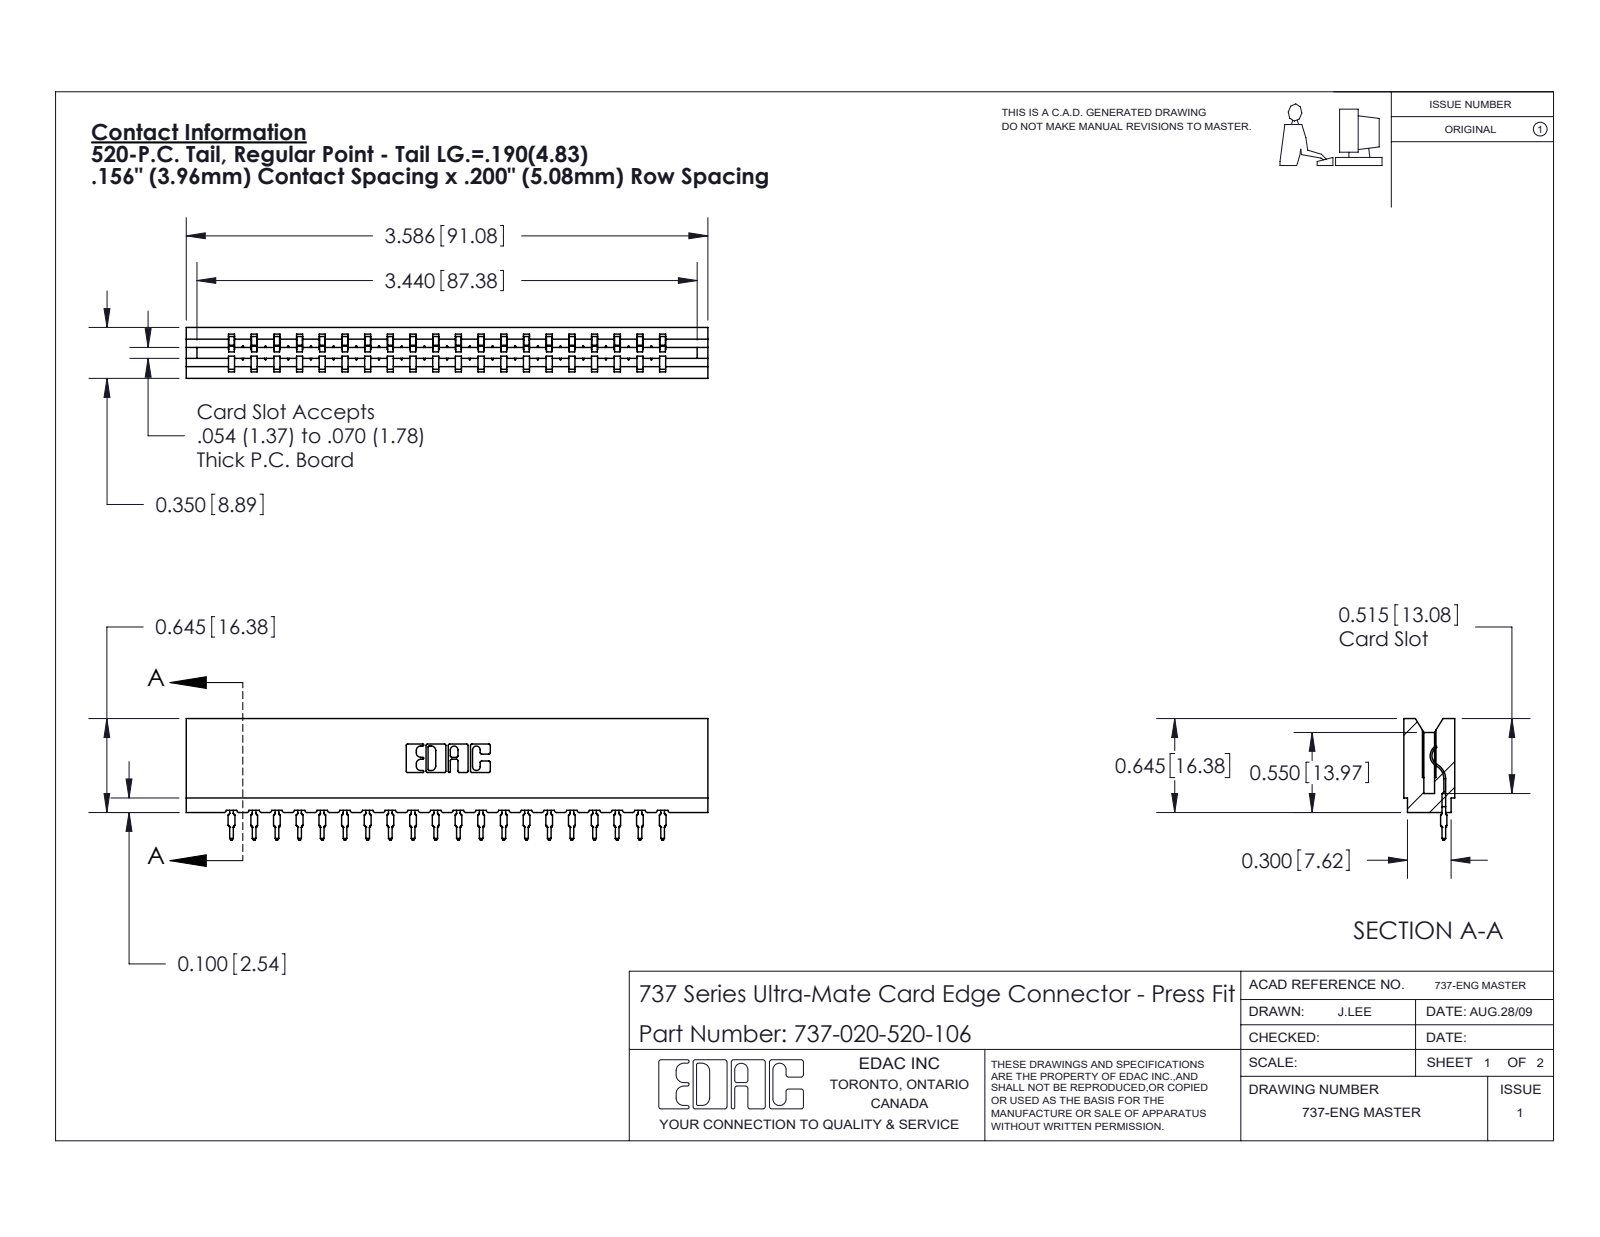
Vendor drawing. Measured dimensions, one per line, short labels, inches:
name: 737-020-520-106; 737 Part_Insulator Option - 06; 745-292-001_520
written by: SolidWorks 2020 (CONFIG_CONTROL_DESIGN)
unit: in
bodies: 21 solids, 2355 faces (1415 planar, 420 cylindrical, 520 other)
size: 3.586 × 0.836 × 0.35
volume: 0.544 in³; area: 17.72 in²
rounds: 40× R0.015, 40× R0.021, 22× R0.01, 6× R0.007, 6× R0.031, 4× R0.005, 4× R0.011, 3× R0.026
face distances: 0.138, 0.212, 0.35, 0.156, 0.624, 0.468, 0.78, 0.074, 0.045, 0.305
